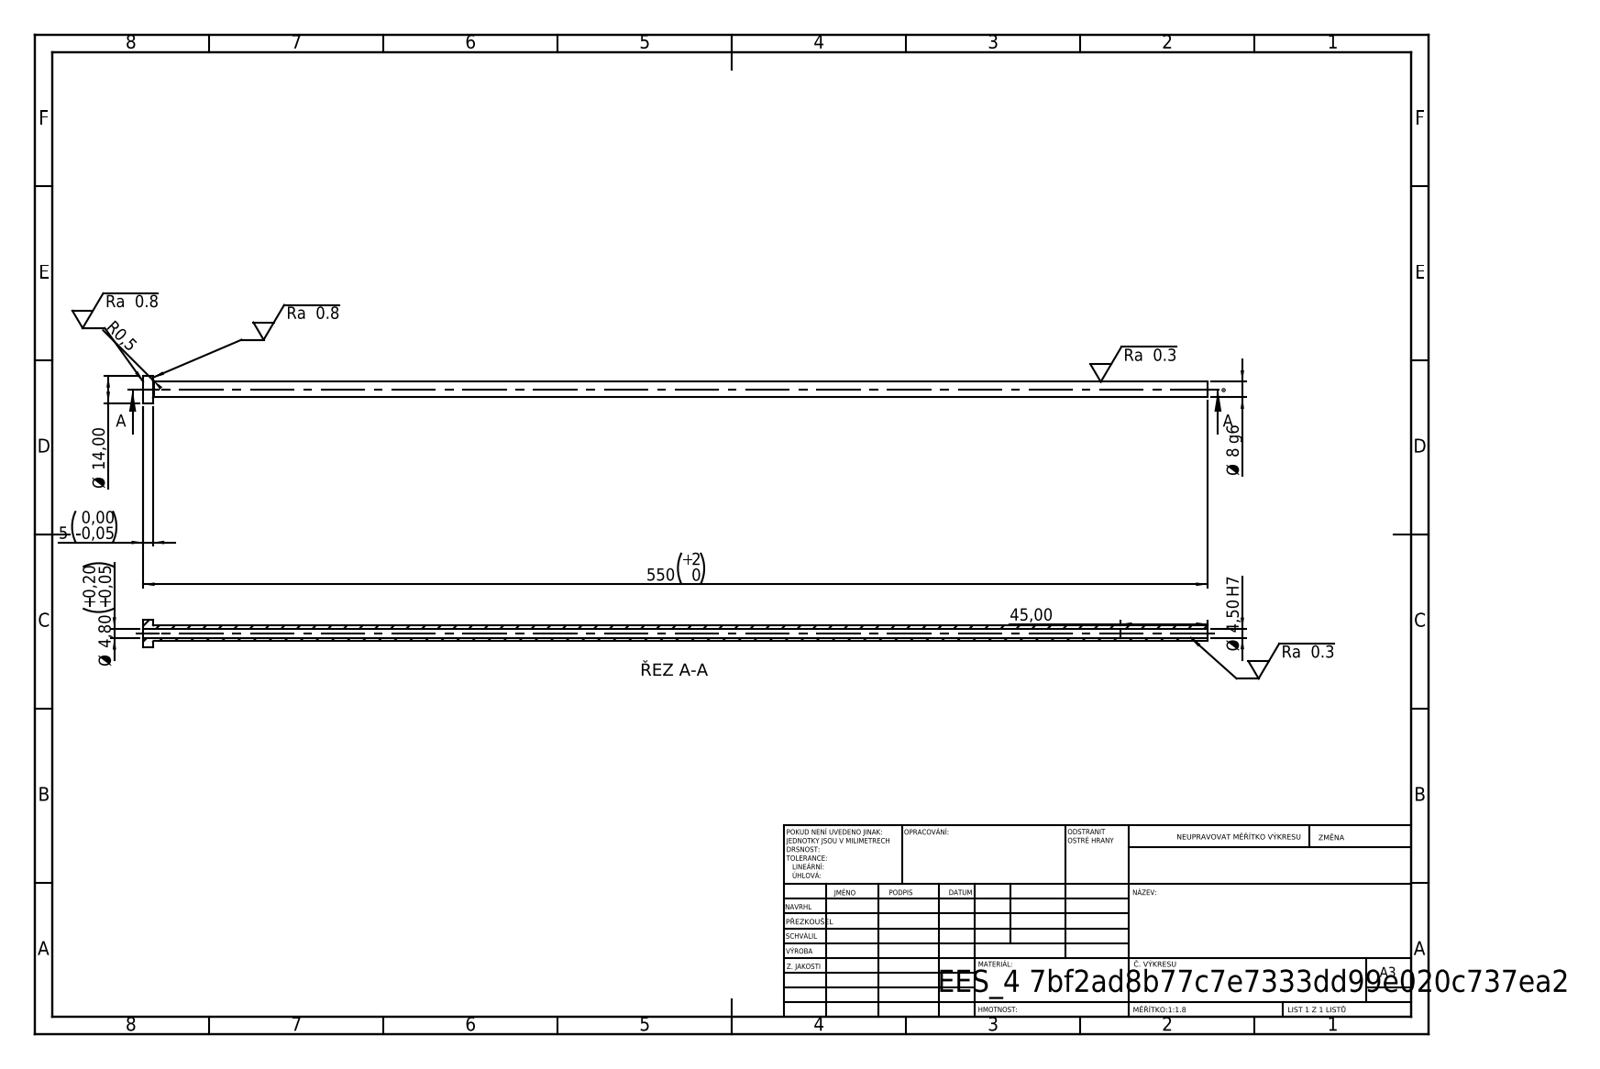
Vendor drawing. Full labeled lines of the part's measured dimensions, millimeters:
STEP written by: SolidWorks 2019 (CONFIG_CONTROL_DESIGN)
Units: millimetres
Bodies: 1 solid, 14 faces (4 planar, 8 cylindrical, 2 other)
Overall size (bounding box): 550 × 14 × 14
Volume: 18 312 mm³ · Surface area: 22 439 mm²
Round holes (diameter × count): ⌀4.5 ×1, ⌀4.8 ×1
Round bosses / shafts (diameter × count): ⌀14 ×1, ⌀8 ×1
Main face-to-face distances: 5, 550, 545, 505, 500, 45
